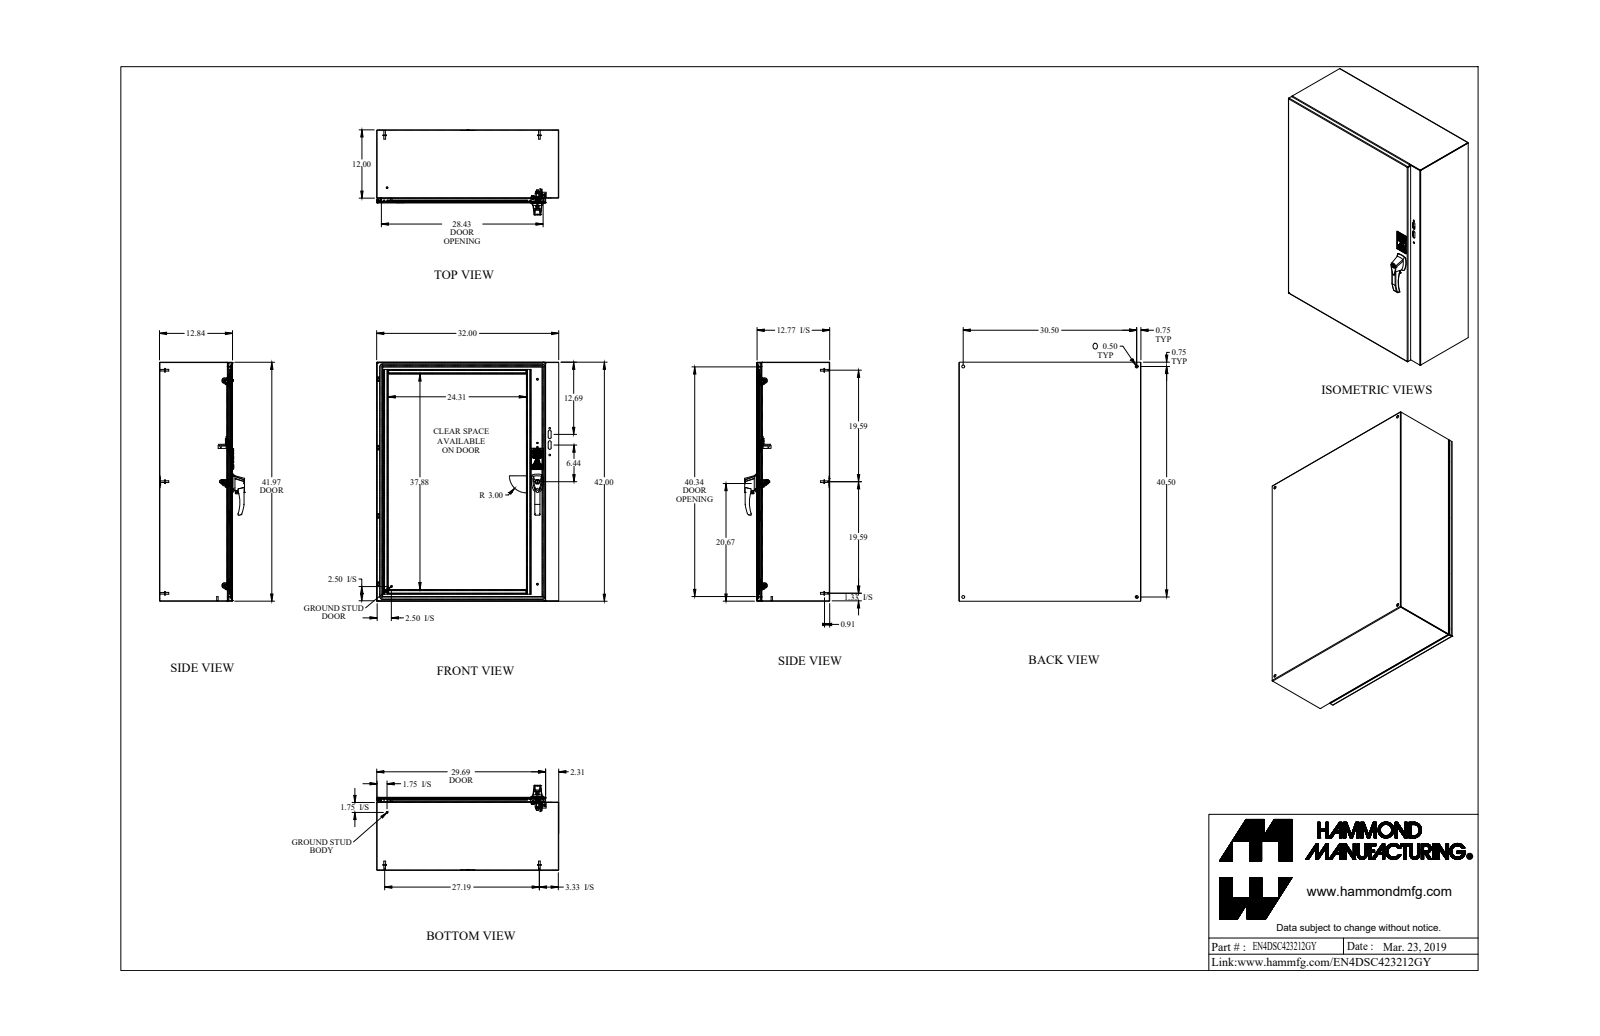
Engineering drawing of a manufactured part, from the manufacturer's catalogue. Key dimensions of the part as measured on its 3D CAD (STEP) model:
Part name (STEP PRODUCT): EN4DSC423212GY
STEP written by: SolidWorks 2019 (AUTOMOTIVE_DESIGN)
Units: inches
Bodies: 69 solids, 1383 faces (800 planar, 413 cylindrical, 170 other)
Overall size (bounding box): 42 × 32 × 14.952
Volume: 382.2 in³ · Surface area: 10 485 in²
Round holes (diameter × count): ⌀0.176 ×6, ⌀0.5 ×4, ⌀0.25 ×3, ⌀0.265 ×3, ⌀0.413 ×3, ⌀0.156 ×2, ⌀0.173 ×2, ⌀0.196 ×2, ⌀0.215 ×2, ⌀0.256 ×2, ⌀0.281 ×2, ⌀0.313 ×2
Round bosses / shafts (diameter × count): ⌀0.25 ×9, ⌀0.625 ×6, ⌀0.313 ×6, ⌀0.27 ×6, ⌀0.156 ×6, ⌀0.375 ×5, ⌀1 ×3, ⌀0.63 ×2
Partial cylindrical surfaces — rounded edges, fillets, slot ends (radius × count): R0.043 ×24, R0.081 ×24, R0.036 ×18, R0.108 ×18, R0.25 ×15, R0.03 ×14, R0.125 ×14, R0.006 ×8
Main face-to-face distances: 0.072, 12.765, 12.693, 12.837, 31.928, 41.928, 31.856, 32, 41.856, 42
Hole centre spacings: 18, 1.11, 18, 18.001, 27.596, 30.5, 36.001, 40.5
